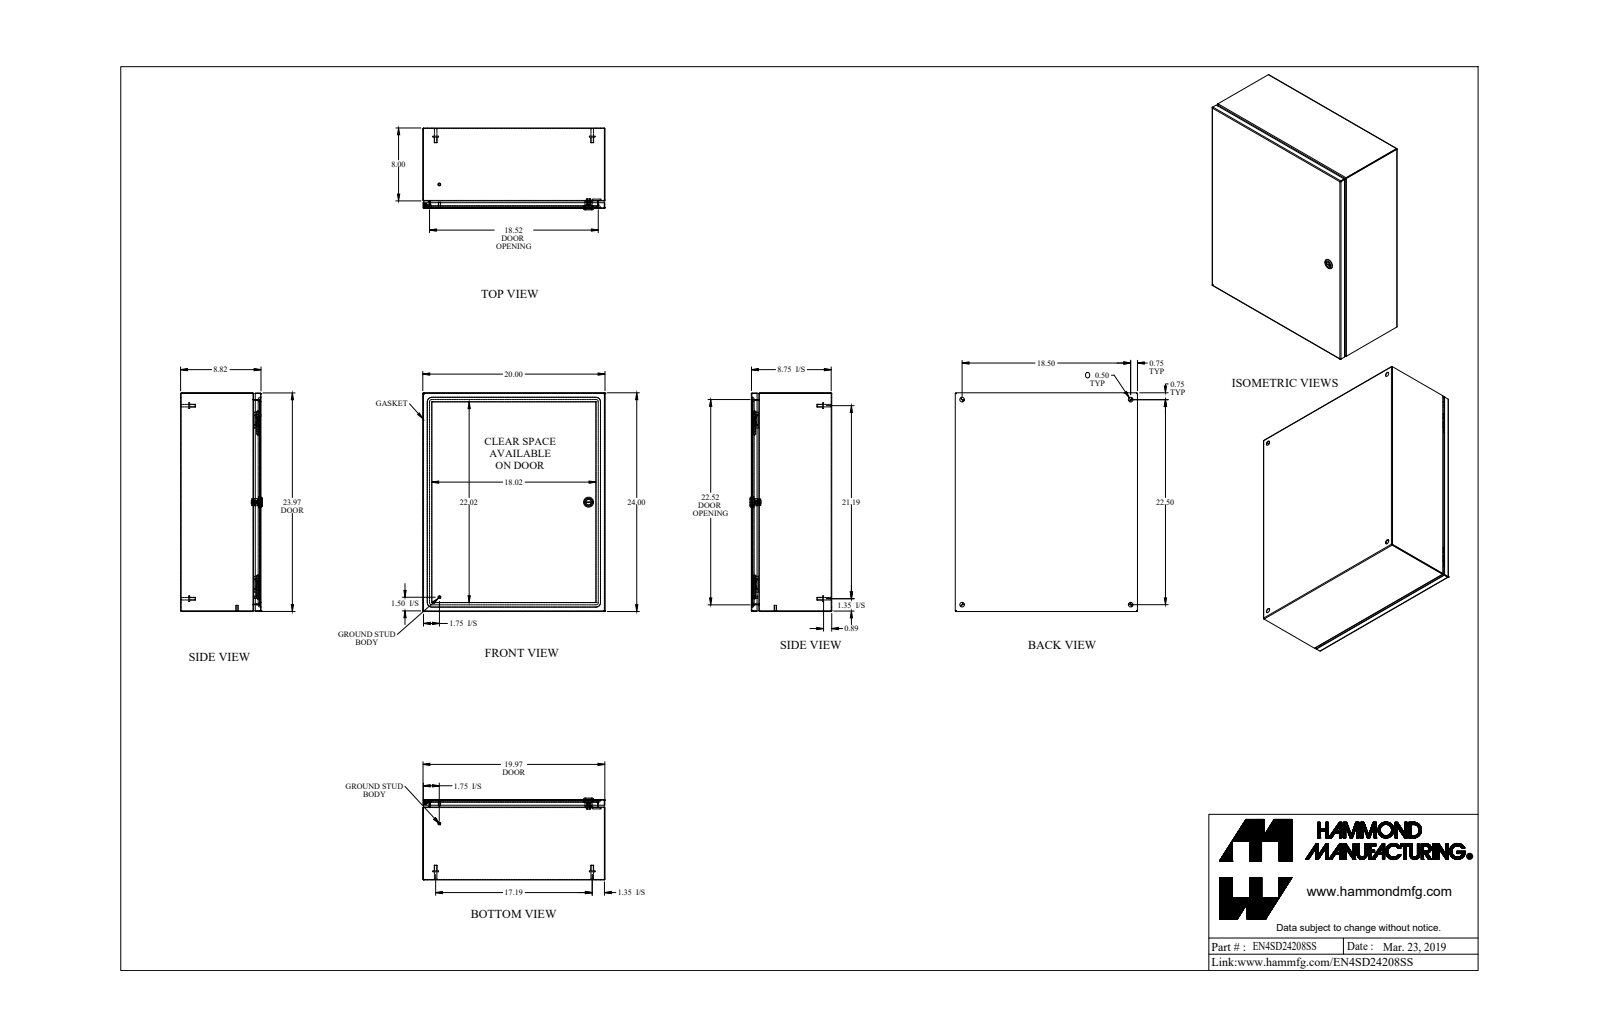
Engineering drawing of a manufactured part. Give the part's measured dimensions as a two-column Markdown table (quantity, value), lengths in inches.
| quantity | value |
| --- | --- |
| part name | EN4SD24208SS_Default |
| STEP written by | SolidWorks 2019 (CONFIG_CONTROL_DESIGN) |
| units | inches |
| bodies | 22 solids, 657 faces (303 planar, 212 cylindrical, 142 other) |
| overall size | 24 × 20 × 8.982 |
| volume | 113.2 in³ |
| surface area | 3 868 in² |
| round holes (diameter × count) | 0.5 × 5, 0.172 × 1, 0.197 × 1, 0.24 × 1, 0.242 × 1, 0.387 × 1, 0.63 × 1, 0.768 × 1 |
| round bosses / shafts (diameter × count) | 0.313 × 6, 0.625 × 5, 0.275 × 4, 0.25 × 2, 1.1 × 1, 0.785 × 1, 0.525 × 1, 0.455 × 1 |
| partial cylindrical surfaces (radius × count) | 0.029 × 21, 0.086 × 21, 0.188 × 12, 0.006 × 4, 0.062 × 4, 0.25 × 4, 0.499 × 4, 0.125 × 2 |
| main face-to-face distances | 0.057, 8.765, 8.708, 8.822, 19.943, 23.943, 19.886, 20, 23.886, 24 |
| hole center spacings | 11.3, 18.5, 20.754, 22.5, 29.129 |
